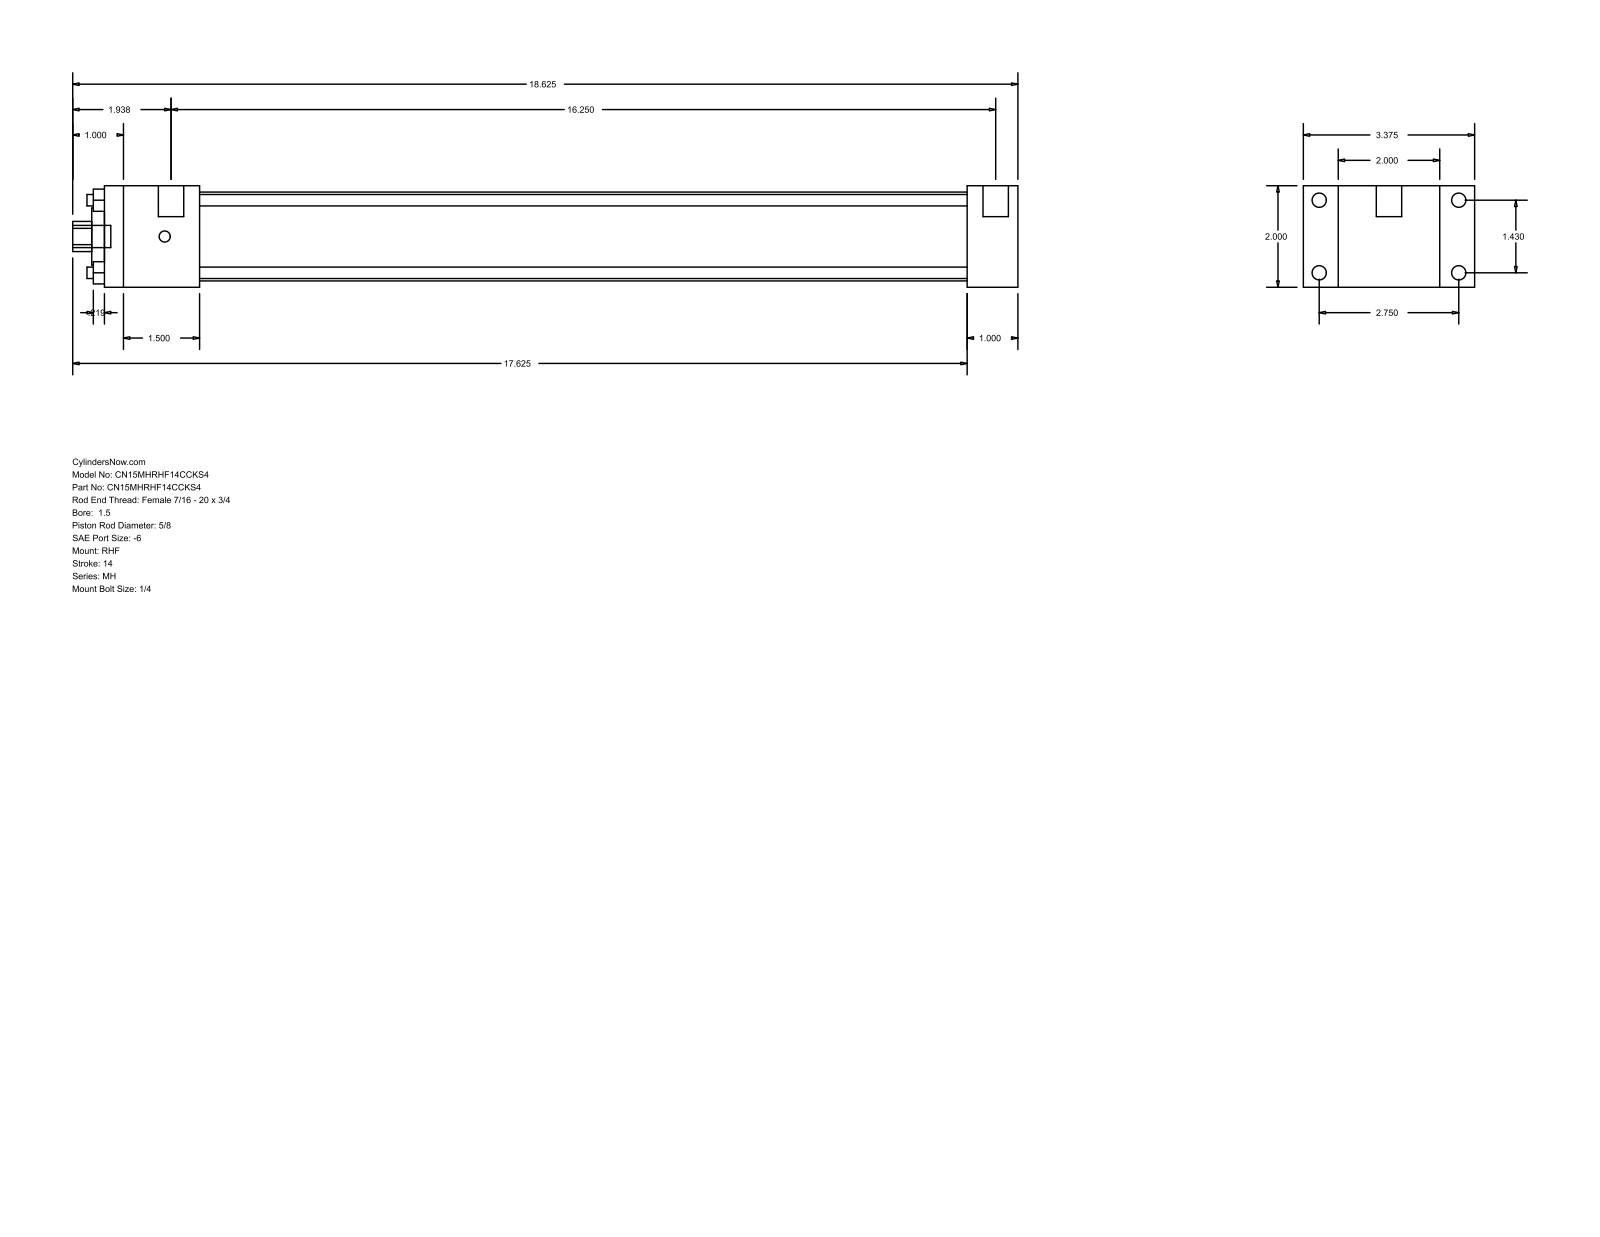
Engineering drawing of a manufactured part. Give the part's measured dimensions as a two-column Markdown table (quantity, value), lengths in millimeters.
| quantity | value |
| --- | --- |
| part name | MH_RHF__0150_0.625 |
| STEP written by | GSSL Pune (CONFIG_CONTROL_DESIGN) |
| units | millimeters |
| bodies | 0 solids, 88 faces (60 planar, 28 cylindrical, 0 other) |
| overall size | 473.07 × 85.72 × 50.8 |
| round holes (diameter × count) | 5.71 × 4, 15.88 × 1, 28.57 × 1, 44.45 × 1 |
| round bosses / shafts (diameter × count) | 7.14 × 4, 5.56 × 4, 12.7 × 2, 11.11 × 1 |
| partial cylindrical surfaces (radius × count) | 7.54 × 1 |
| main face-to-face distances | 50.8, 17.46, 68.26, 25.39, 431.8, 457.19, 85.72, 47.62, 384.18, 409.57 |
| hole center spacings | 25.68, 36.32, 51.36 |
